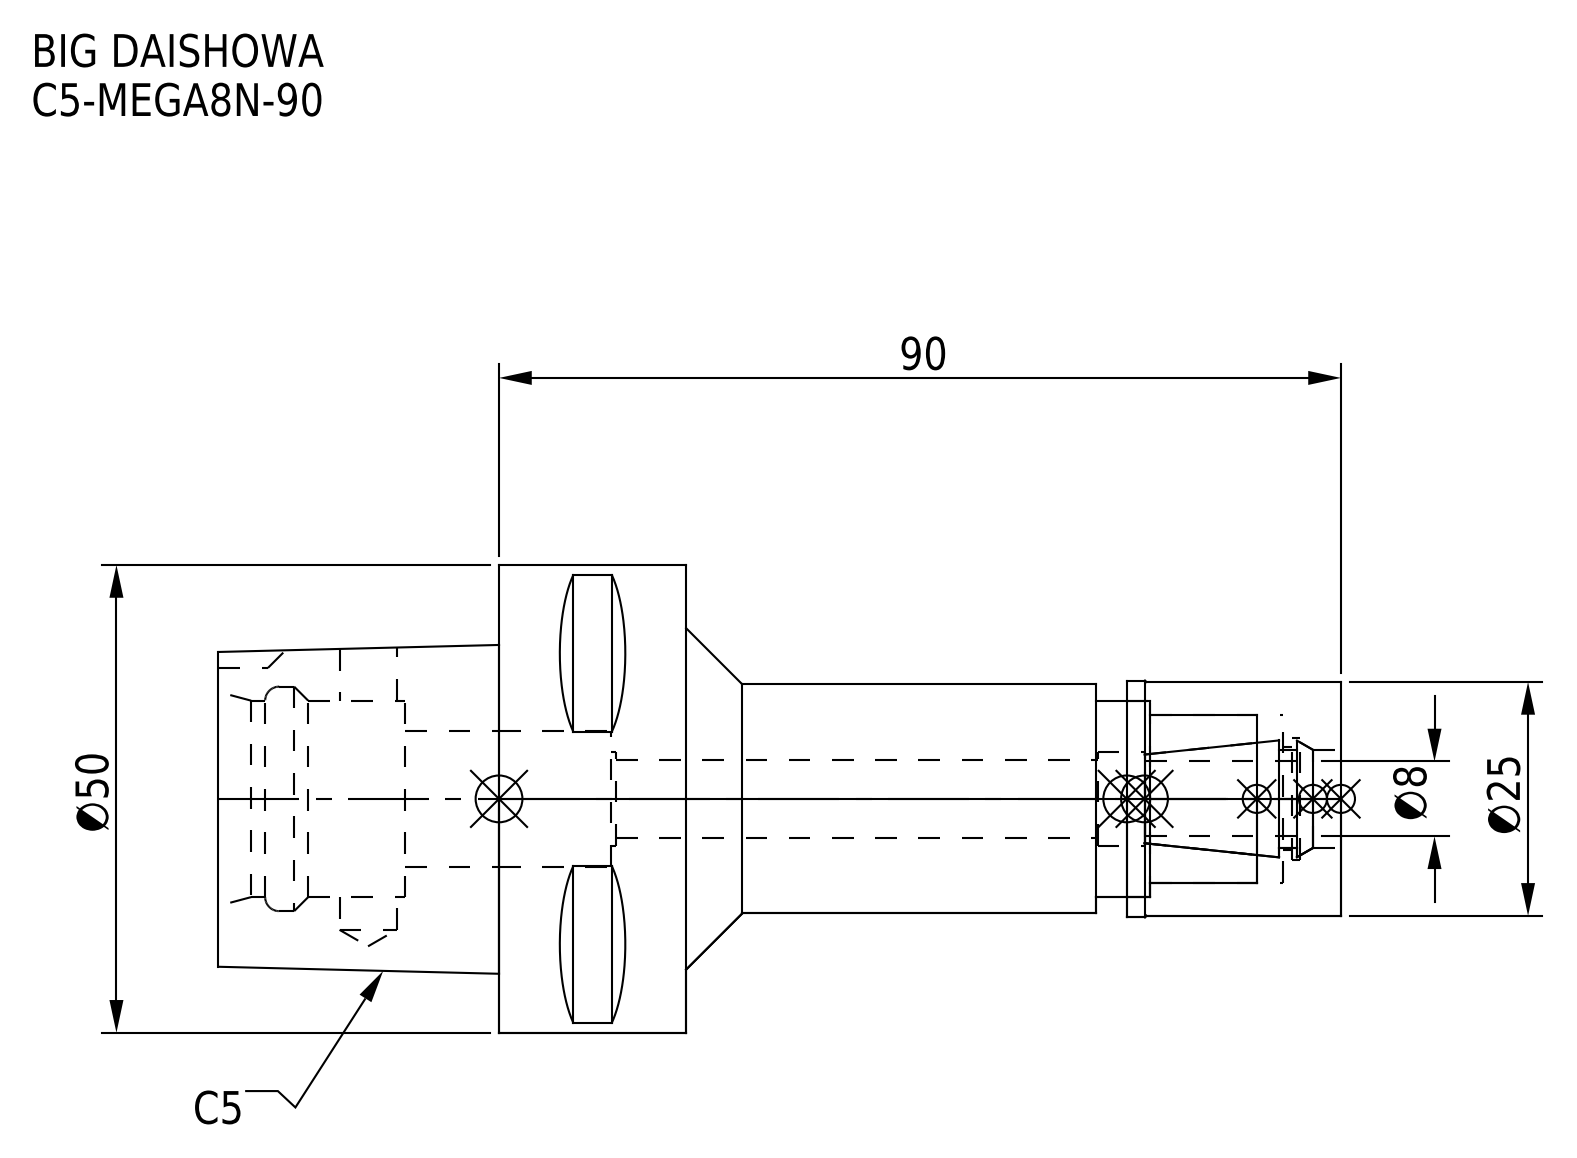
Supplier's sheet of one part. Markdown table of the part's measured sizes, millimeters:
| quantity | value |
| --- | --- |
| part name | MGN8_1.stp; C5-MEGA8N-90_1.stp; DXF_TEMP_ASSY_ASM_4_ASM.stp; C5-MEGA8N-90-080_ASM.stp (+3 more) |
| STEP written by | SolidWorks 2019 (CONFIG_CONTROL_DESIGN) |
| units | millimeters |
| bodies | 2 solids, 98 faces (39 planar, 41 cylindrical, 18 other) |
| overall size | 120 × 50 × 50 |
| volume | 83 469 mm³ |
| surface area | 22 812 mm² |
| round holes (diameter × count) | 6.1 × 1, 8.4 × 1, 10 × 1, 10.5 × 1, 11 × 1, 13 × 1, 14.5 × 1, 18 × 1, 21 × 1, 24 × 1 |
| round bosses / shafts (diameter × count) | 50 × 1, 25.3 × 1, 25 × 1, 24.5 × 1 |
| partial cylindrical surfaces (radius × count) | 4 × 1 |
| main face-to-face distances | 20, 30, 70, 90, 120, 50, 63.8, 93.8, 44, 20.4 |
